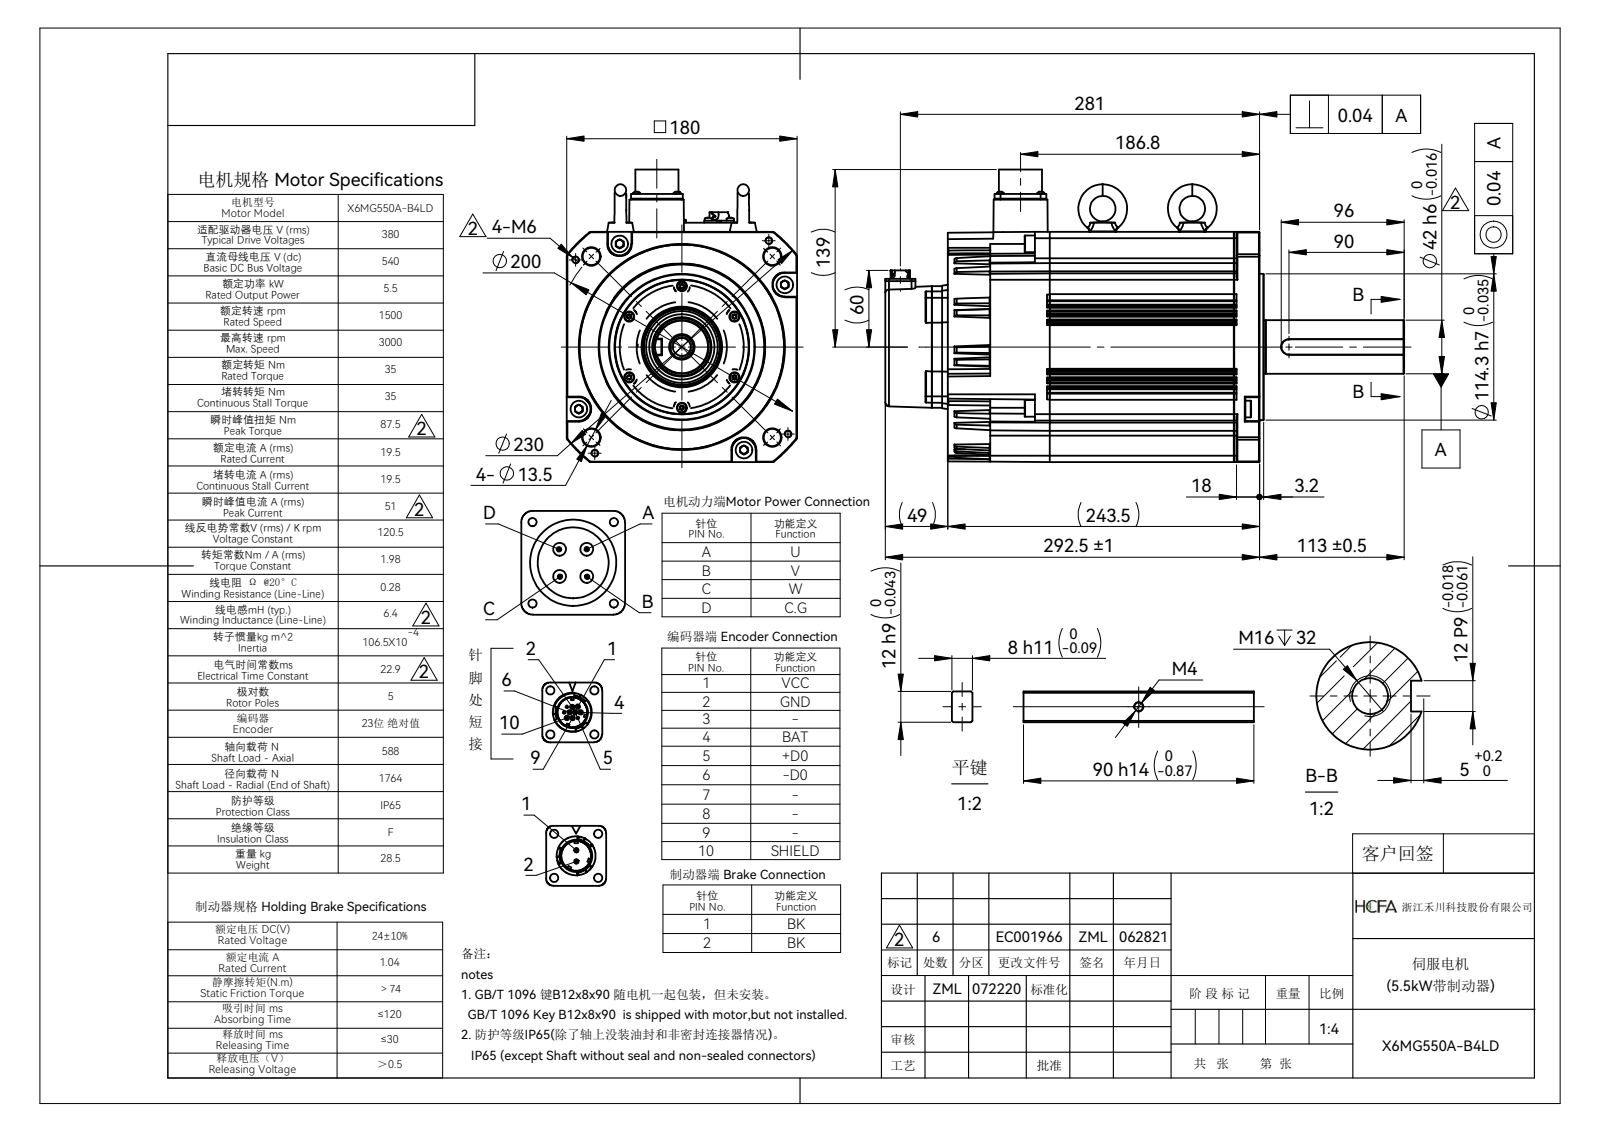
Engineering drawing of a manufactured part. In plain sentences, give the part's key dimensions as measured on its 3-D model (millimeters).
The part is named "SV-X6MG550A-B4LD". Its 3-D file was written by "SolidWorks 2016 (CONFIG_CONTROL_DESIGN)". It is 1 solid with 1826 faces: 699 planar, 623 cylindrical and 504 other. Overall it measures 405.5 by 228.6 by 180 millimeters. Its volume is 7 270 000 cubic millimeters and its surface area 317 753 square millimeters. Round holes: 4 of diameter 13.5, 1 of diameter 11.6, 1 of diameter 11.75, 1 of diameter 14, 1 of diameter 27.7. Round bosses or shafts: 6 of diameter 13, 4 of diameter 5.7, 4 of diameter 5.6, 4 of diameter 5, 2 of diameter 15.2, 2 of diameter 0.75, 1 of diameter 114.3, 1 of diameter 42. Partial cylindrical surfaces (rounded edges, fillets, slot ends): 98 of radius 0.5, 42 of radius 1, 27 of radius 5, 16 of radius 2, 12 of radius 3, 8 of radius 2.8, 6 of radius 0.32, 6 of radius 1.15. The main face-to-face distances are 180, 32.5, 147.5, 243.5, 115, 246.7, 3.2, 292.5, 49, 295.7. The hole center spacings are 100, 141.42, 200, 48.75.
